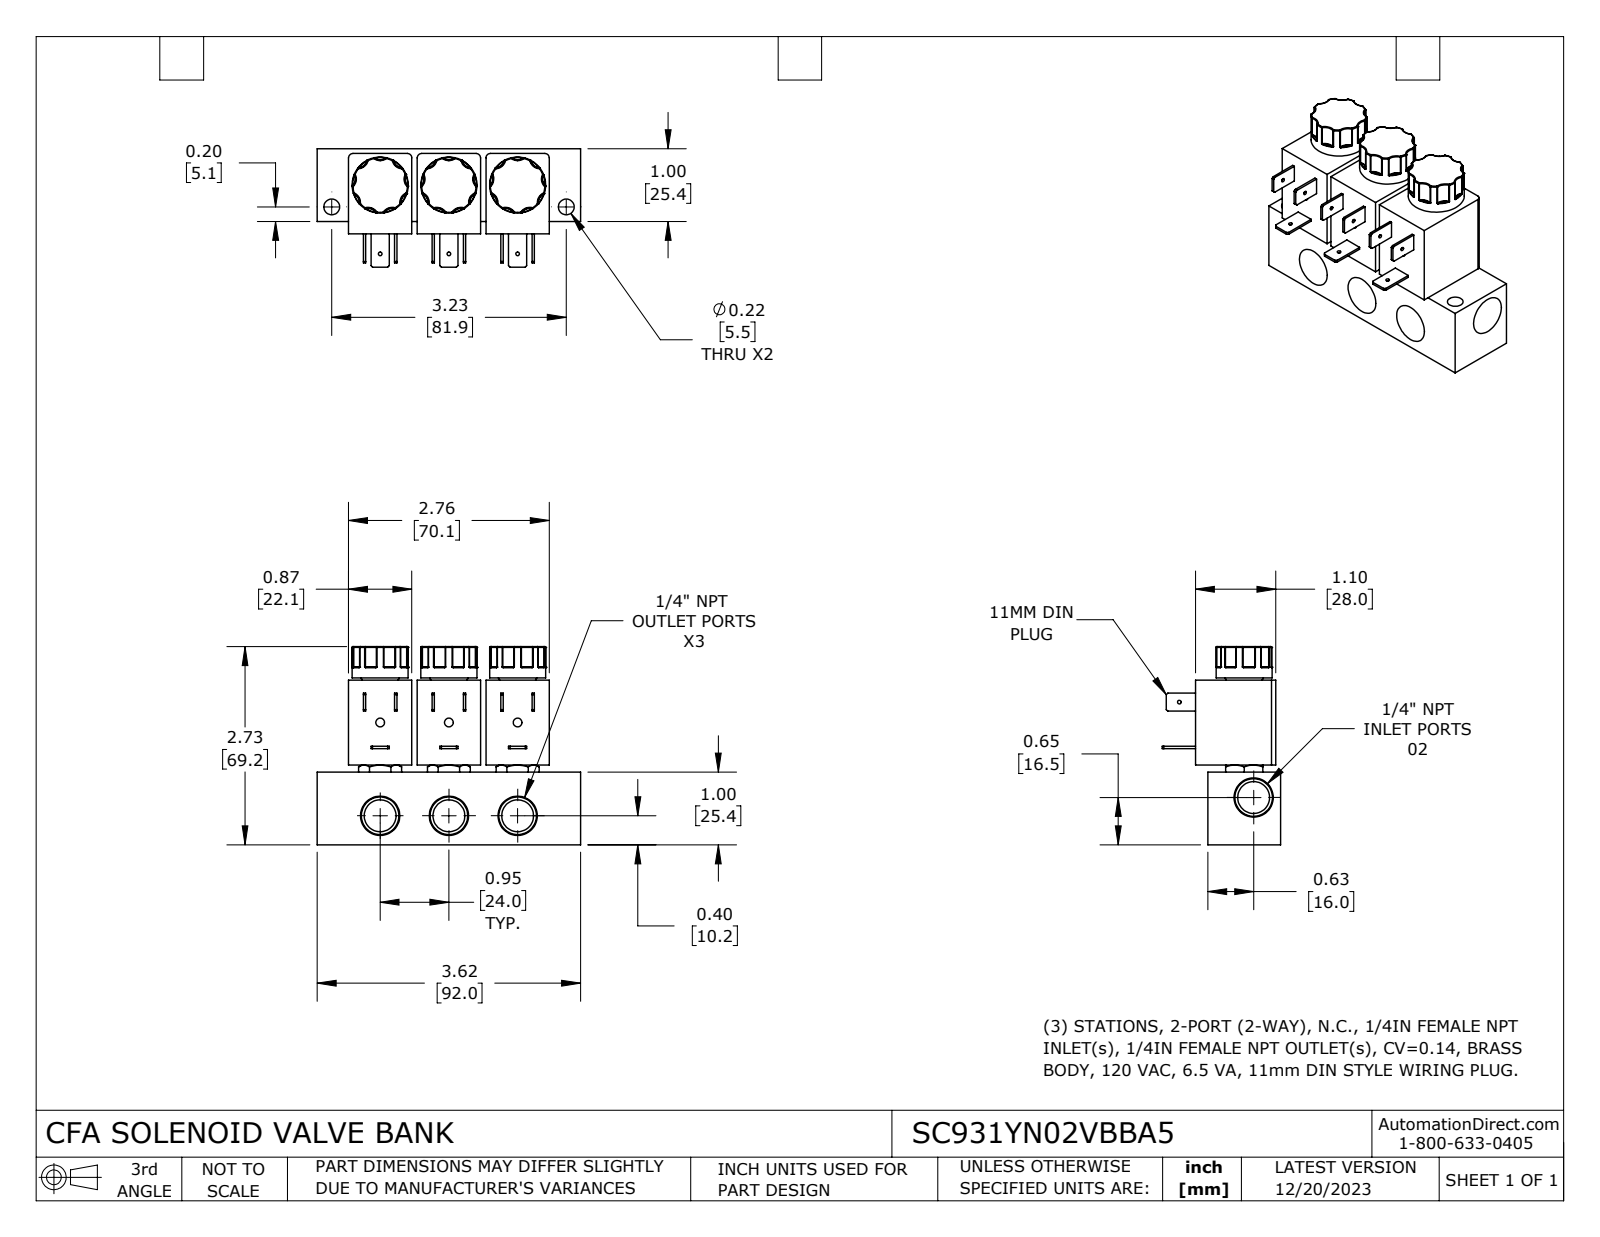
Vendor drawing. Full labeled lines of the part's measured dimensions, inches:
Part name (STEP PRODUCT): SC931YN02VBBA5
STEP written by: SolidWorks 2023 (CONFIG_CONTROL_DESIGN)
Units: inches
Bodies: 1 solid, 657 faces (146 planar, 140 cylindrical, 371 other)
Overall size (bounding box): 3.622 × 2.725 × 1.627
Volume: 7.008 in³ · Surface area: 47.81 in²
Round holes (diameter × count): ⌀0.05 ×4, ⌀0.438 ×4, ⌀0.12 ×3, ⌀0.217 ×2
Round bosses / shafts (diameter × count): ⌀0.77 ×3
Partial cylindrical surfaces — rounded edges, fillets, slot ends (radius × count): R0.01 ×54, R0.133 ×25, R0.06 ×6, R0.132 ×2
Main face-to-face distances: 1, 0.945, 0.87, 1.169, 0.169, 0.065, 0.935, 1.104, 1.89, 1.815
Hole centre spacings: 0.945, 1.593, 1.282, 1.89, 2.283, 0.928, 0.93, 1.662
